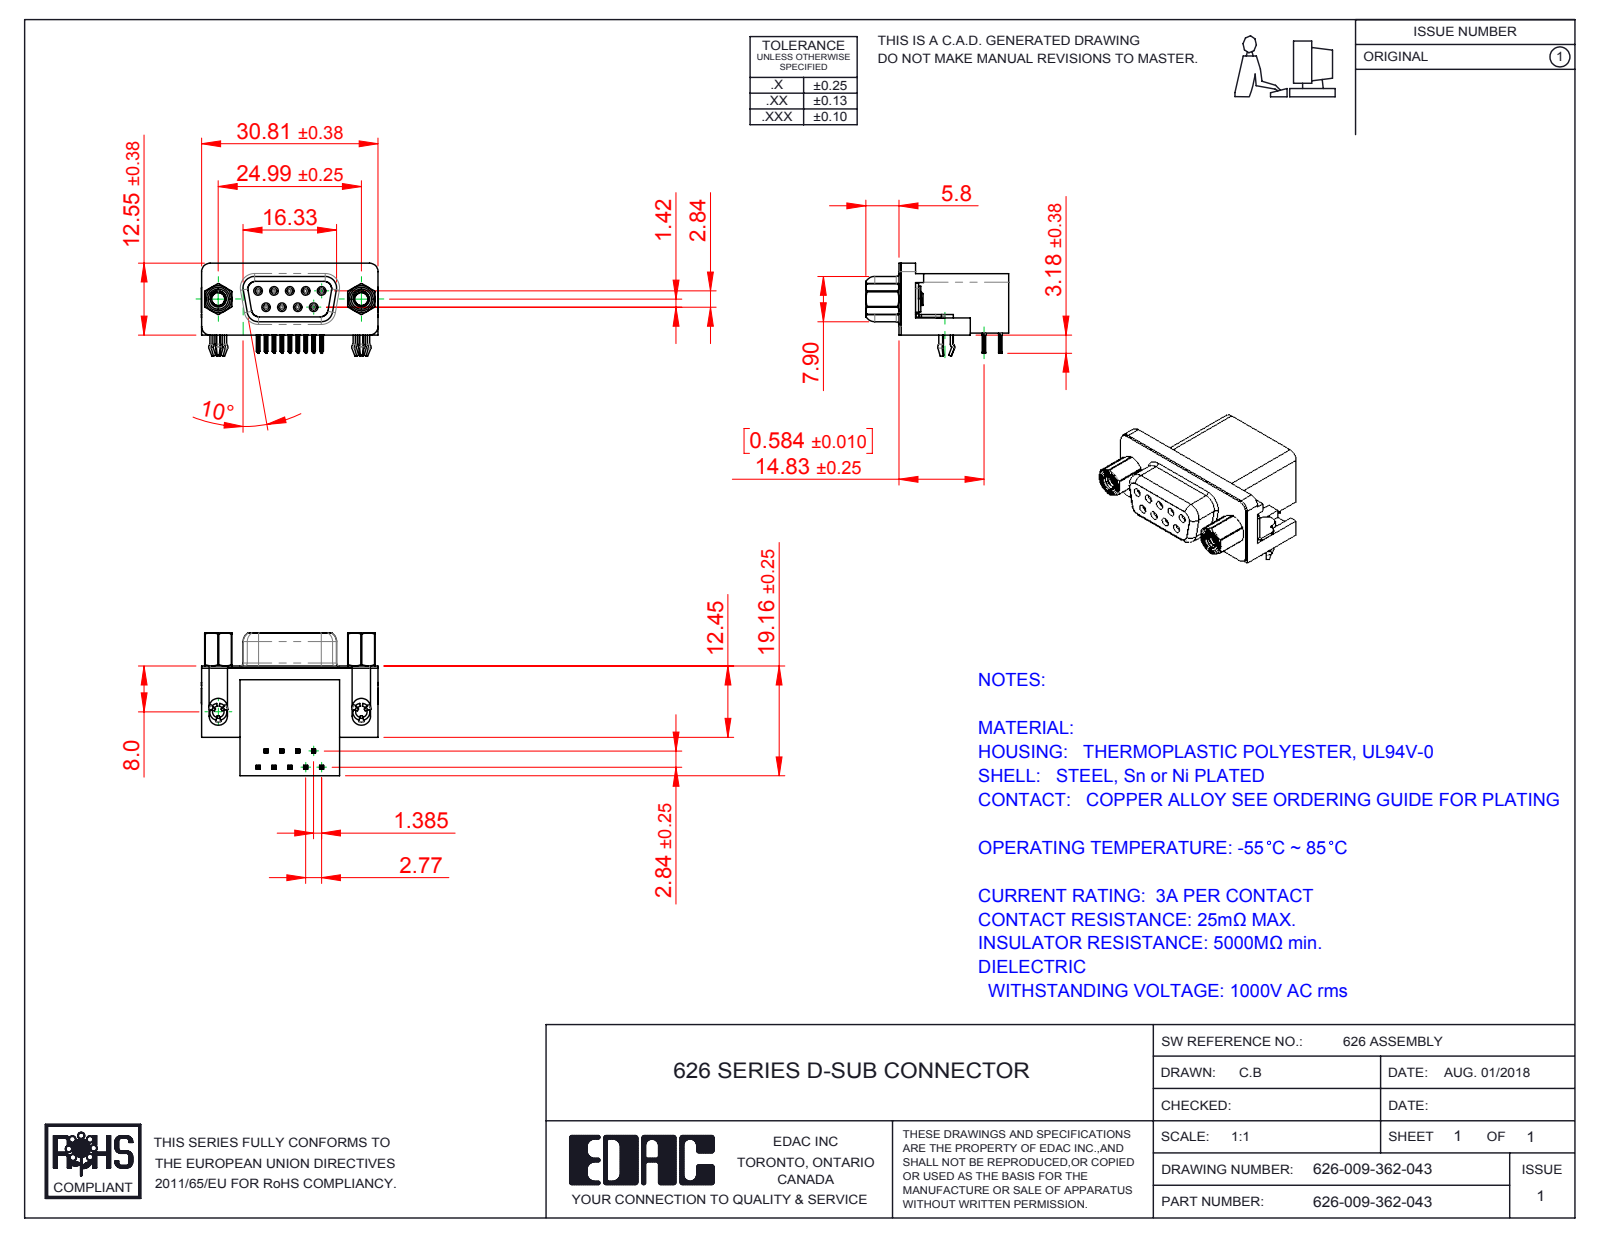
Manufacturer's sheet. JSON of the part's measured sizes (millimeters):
{"part_name": "626 4-40 Hex Standoff 5; 626 Housing_9 Socket; 626-009-362-043; 626 Round Threaded Standoff (+4 more)", "step_written_by": "SolidWorks 2016 (CONFIG_CONTROL_DESIGN)", "units": "millimeters", "bodies": {"solids": 17, "faces": 1796, "planar": 736, "cylindrical": 502, "other": 558}, "overall_size": [30.89, 24.96, 16.25], "volume_mm3": 5280, "surface_area_mm2": 6534, "round_holes": [[0.8, 9], [0.9, 9], [2, 2], [2.29, 2], [2.3, 2], [3.1, 2], [4, 2], [4.8, 2], [5, 2]], "round_bosses_or_shafts": [[1.2, 9], [4.9, 2], [4.7, 2], [4.5, 2], [3.85, 2], [3, 2], [2.79, 2]], "partial_cylinders_radius": [[0.1, 72], [0.15, 36], [0.35, 18], [1, 18], [0.34, 9], [1.35, 8], [1.6, 8], [1.5, 7]], "face_to_face_distances": [0.4, 10.34, 0.35, 18.76, 19.16, 16.26, 6.2, 2.9, 2.5, 5.8], "hole_center_spacings": [3.16, 2.77, 5.54, 5.03, 5.04, 8.31, 7.48, 7.49]}
